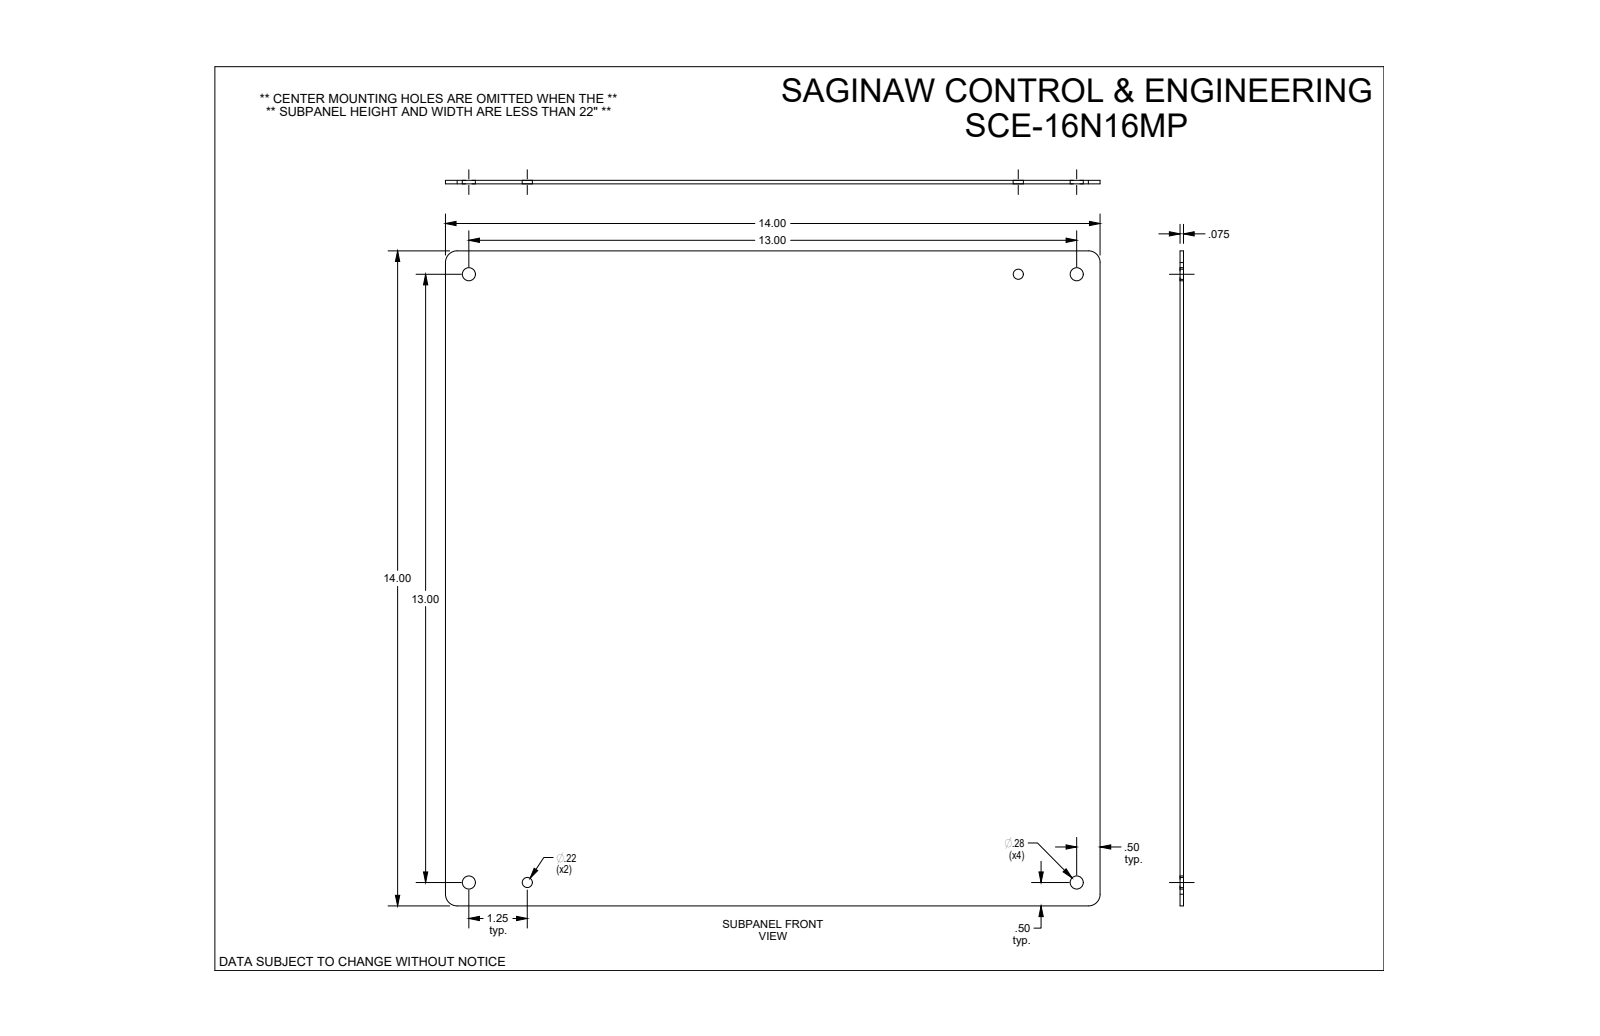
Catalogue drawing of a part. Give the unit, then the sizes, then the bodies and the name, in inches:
Units: inches
Overall size (bounding box): 14 × 14 × 0.075
Round holes (diameter × count): ⌀0.281 ×4, ⌀0.218 ×2
Partial cylindrical surfaces — rounded edges, fillets, slot ends (radius × count): R0.25 ×4
Main face-to-face distances: 0.075, 14
Hole centre spacings: 13, 1.25, 11.75, 13.06, 17.523, 18.385, 16.711
Volume: 14.67 in³ · Surface area: 395.8 in²
Bodies: 1 solid, 16 faces (6 planar, 10 cylindrical, 0 other)
Part name (STEP PRODUCT): SCE-16N16MP
STEP written by: SolidWorks 2019 (CONFIG_CONTROL_DESIGN)
